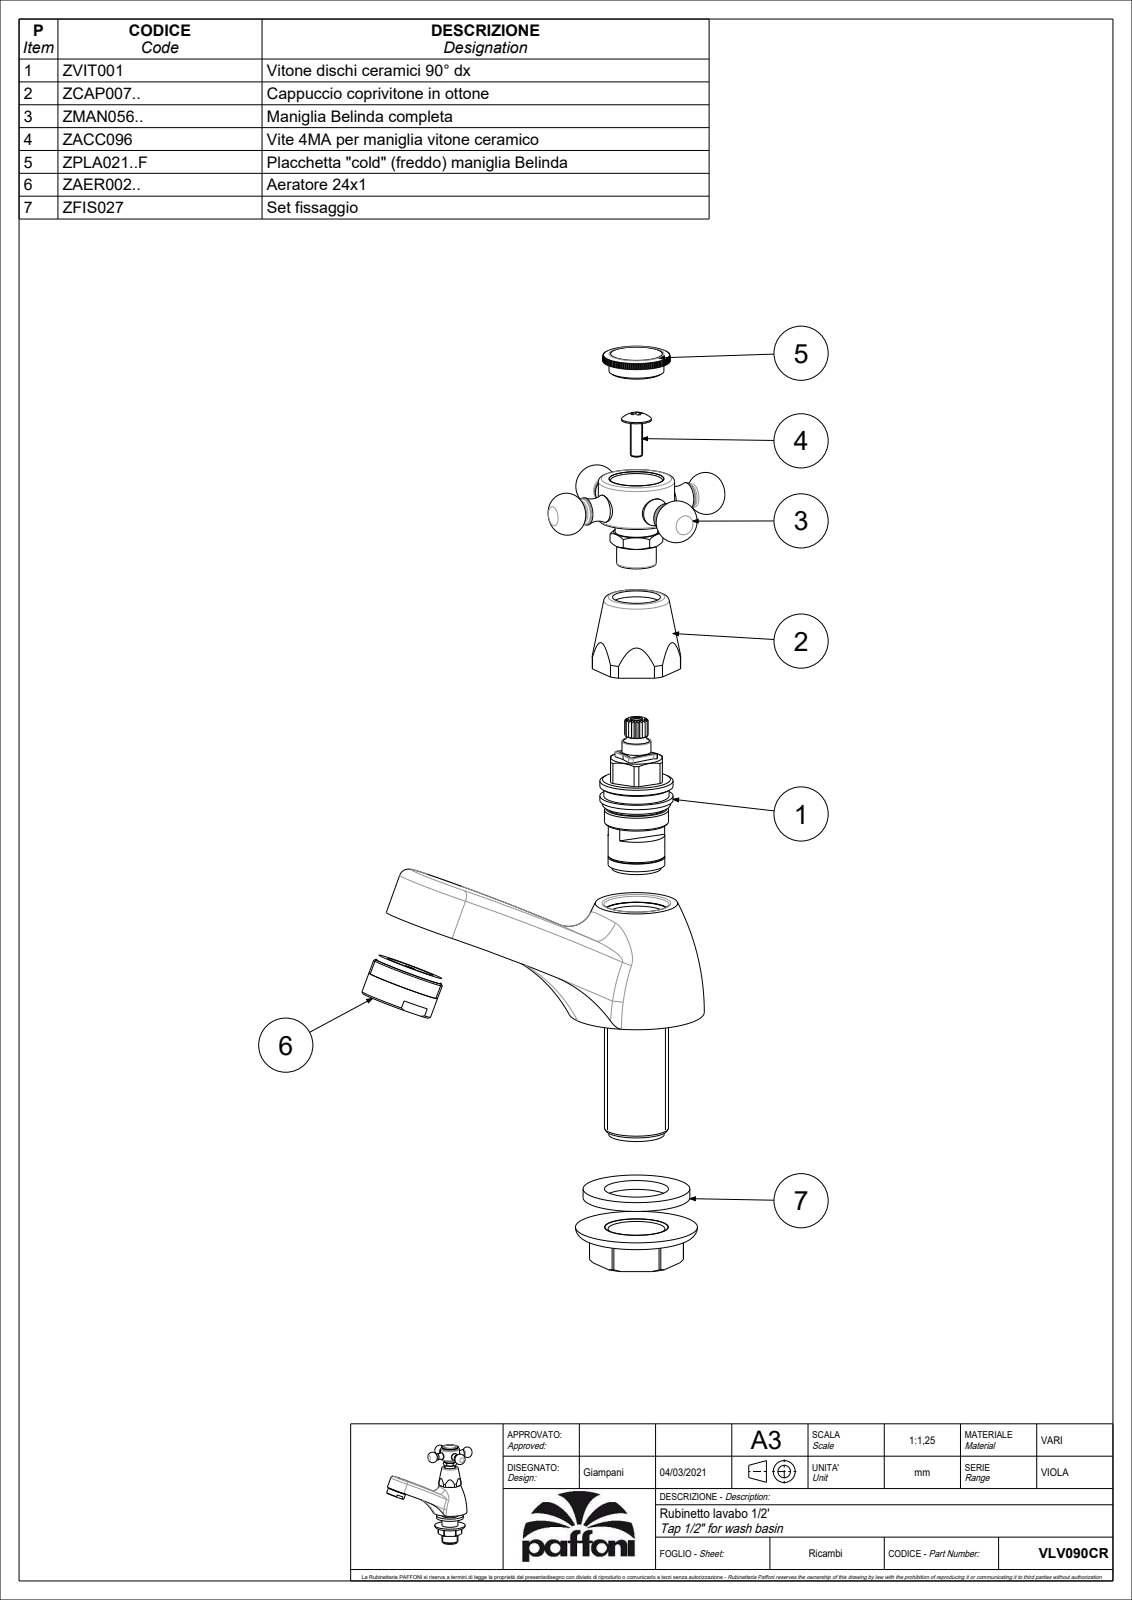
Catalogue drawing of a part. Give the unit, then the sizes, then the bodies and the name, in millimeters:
Units: millimetres
Overall size (bounding box): 125.92 × 88.9 × 64.07
Round bosses / shafts (diameter × count): ⌀9 ×2, ⌀7 ×2, ⌀25 ×1, ⌀24 ×1, ⌀14 ×1, ⌀13 ×1
Partial cylindrical surfaces — rounded edges, fillets, slot ends (radius × count): R11 ×1, R14.5 ×1, R15 ×1, R979.65 ×1, R995.65 ×1
Main face-to-face distances: 30, 72.2, 26.5, 5.75, 20.75, 61, 11.2, 4, 15, 22
Volume: 114 988 mm³ · Surface area: 20 968 mm²
Bodies: 1 solid, 476 faces (242 planar, 143 cylindrical, 91 other)
Part name (STEP PRODUCT): VLV090CR
STEP written by: CREO PARAMETRIC BY PTC INC, 2020044 (CONFIG_CONTROL_DESIGN)
